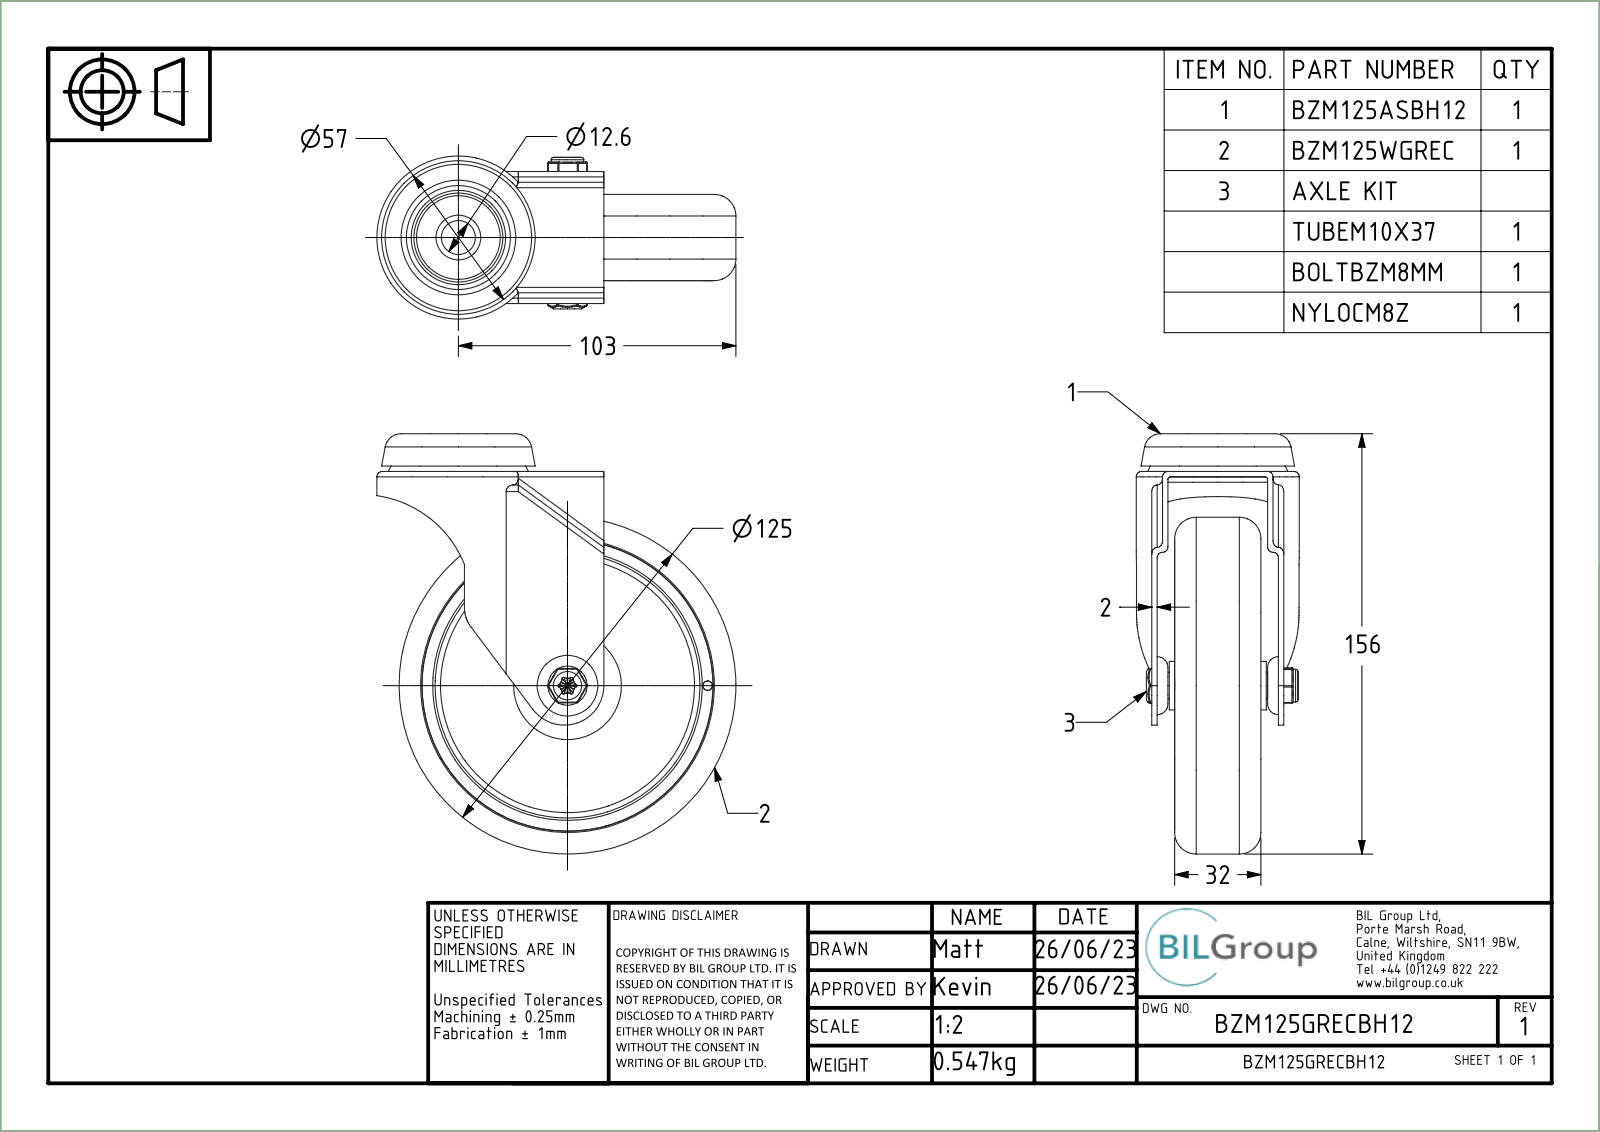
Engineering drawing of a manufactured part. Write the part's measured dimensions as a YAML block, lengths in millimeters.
part_name: "BZM125ASBH12; ZINC PLATED PRESSED STEEL HEAD; ZINC PLATED PRESSED STEEL FORKS; BZM125GRECBH12 (+8 more)"
step_written_by: "Spatial InterOp 3D (CONFIG_CONTROL_DESIGN)"
units: millimeters
bodies: {solids: 9, faces: 384, planar: 70, cylindrical: 172, other: 142}
overall_size: [156, 133.25, 60.5]
volume: 224437
surface_area: 109675
round_holes:
  - {diameter: 3.5, count: 1}
  - {diameter: 8, count: 1}
  - {diameter: 8.2, count: 1}
  - {diameter: 8.5, count: 1}
  - {diameter: 8.6, count: 1}
  - {diameter: 10.1, count: 1}
  - {diameter: 10.3, count: 1}
  - {diameter: 12.6, count: 1}
  - {diameter: 46, count: 1}
  - {diameter: 108, count: 1}
round_bosses_or_shafts:
  - {diameter: 125, count: 1}
  - {diameter: 48, count: 1}
  - {diameter: 30, count: 1}
  - {diameter: 18, count: 1}
  - {diameter: 12.1, count: 1}
  - {diameter: 10, count: 1}
  - {diameter: 6, count: 1}
partial_cylinders:
  - {radius: 0.5, count: 30}
  - {radius: 2, count: 22}
  - {radius: 1, count: 2}
  - {radius: 2.75, count: 1}
  - {radius: 12, count: 1}
  - {radius: 14.65, count: 1}
  - {radius: 28.25, count: 1}
  - {radius: 30.25, count: 1}
face_to_face_distances: [4, 2, 22.5, 20.5, 26.5, 14, 47, 24.5, 18, 6.5]
hole_center_spacings: [52]
